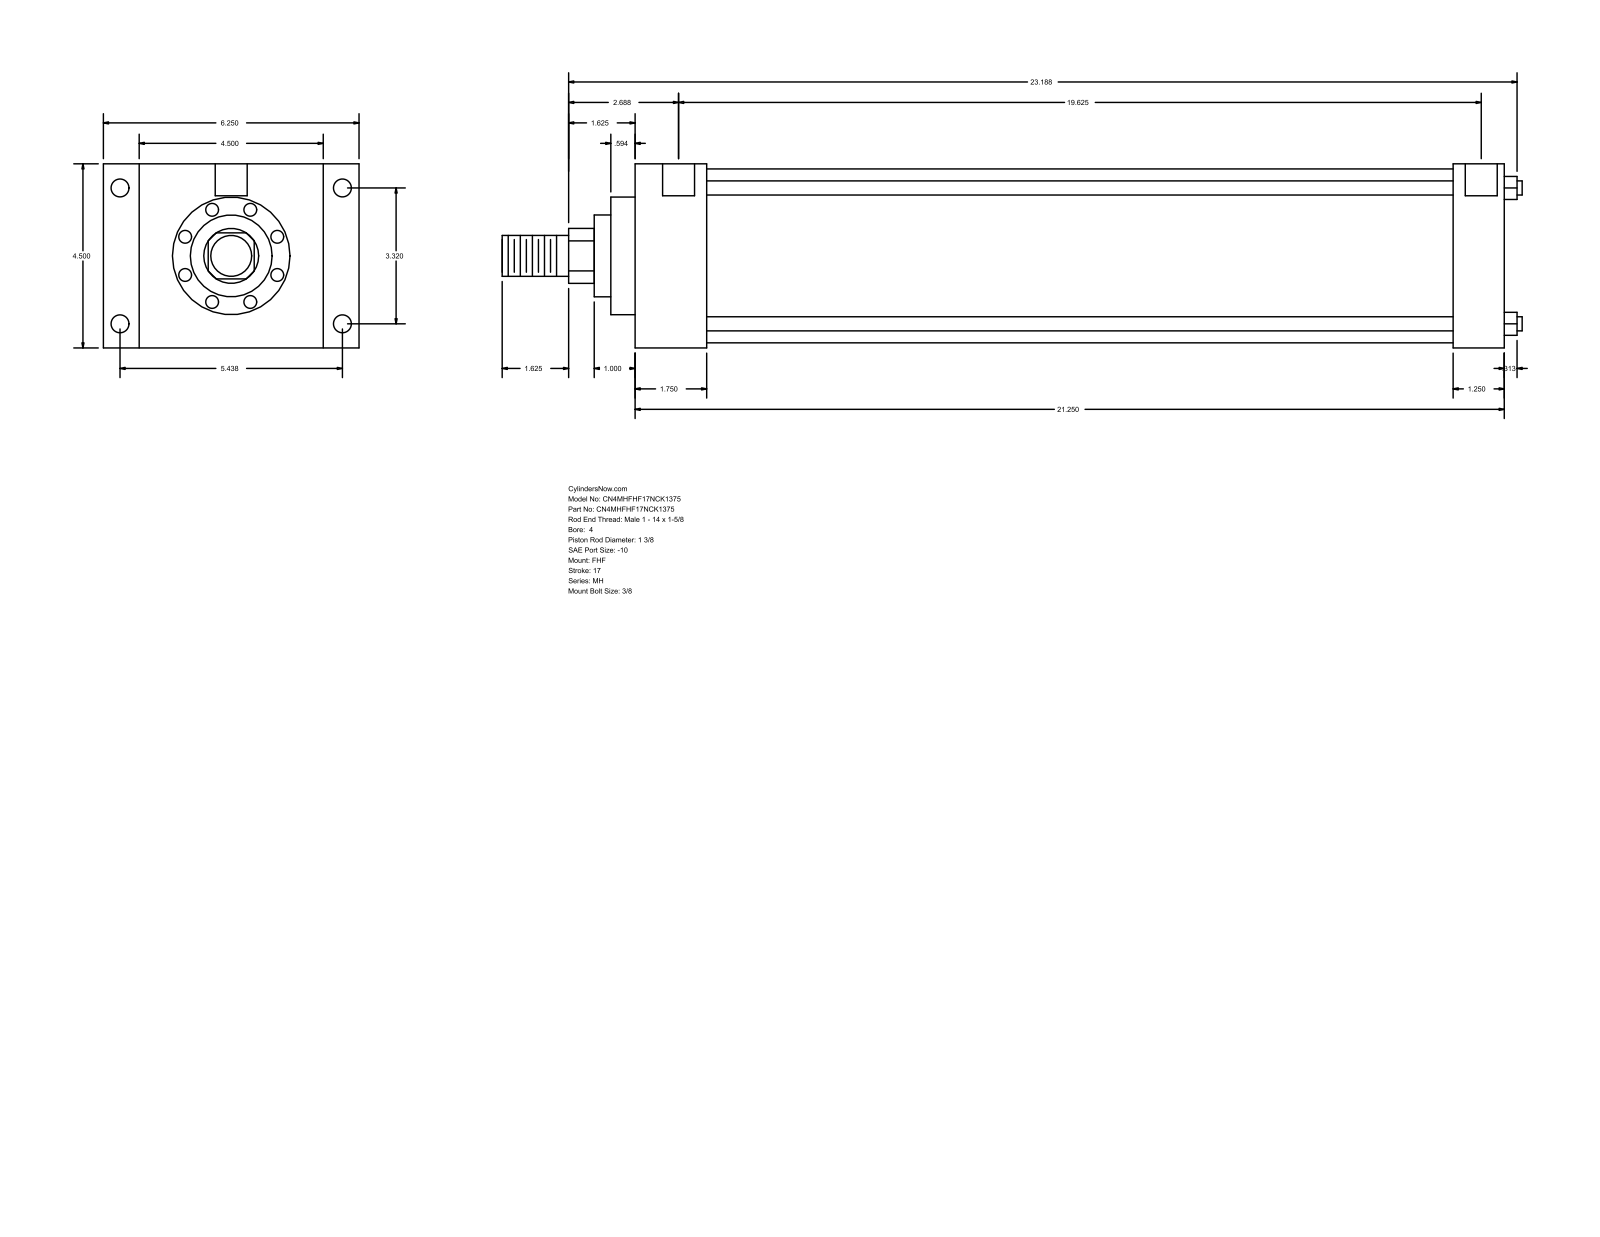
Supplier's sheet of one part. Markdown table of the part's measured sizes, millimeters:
| quantity | value |
| --- | --- |
| part name | MH_FHF__0400_1.375 |
| STEP written by | GSSL Pune (CONFIG_CONTROL_DESIGN) |
| units | millimeters |
| bodies | 0 solids, 90 faces (61 planar, 29 cylindrical, 0 other) |
| overall size | 633.41 × 158.75 × 114.3 |
| round holes (diameter × count) | 8.73 × 4, 11.13 × 4, 19.84 × 2 |
| round bosses / shafts (diameter × count) | 8.76 × 4, 107.95 × 1, 73.03 × 1, 50.8 × 1, 34.92 × 1, 25.4 × 1 |
| partial cylindrical surfaces (radius × count) | 17.06 × 1 |
| main face-to-face distances | 114.3, 539.75, 44.45, 495.3, 22.23, 136.53, 158.76, 508, 463.55, 31.75 |
| hole center spacings | 1.59, 84.32, 138.12, 161.82, 500.07, 501.66, 498.48 |
